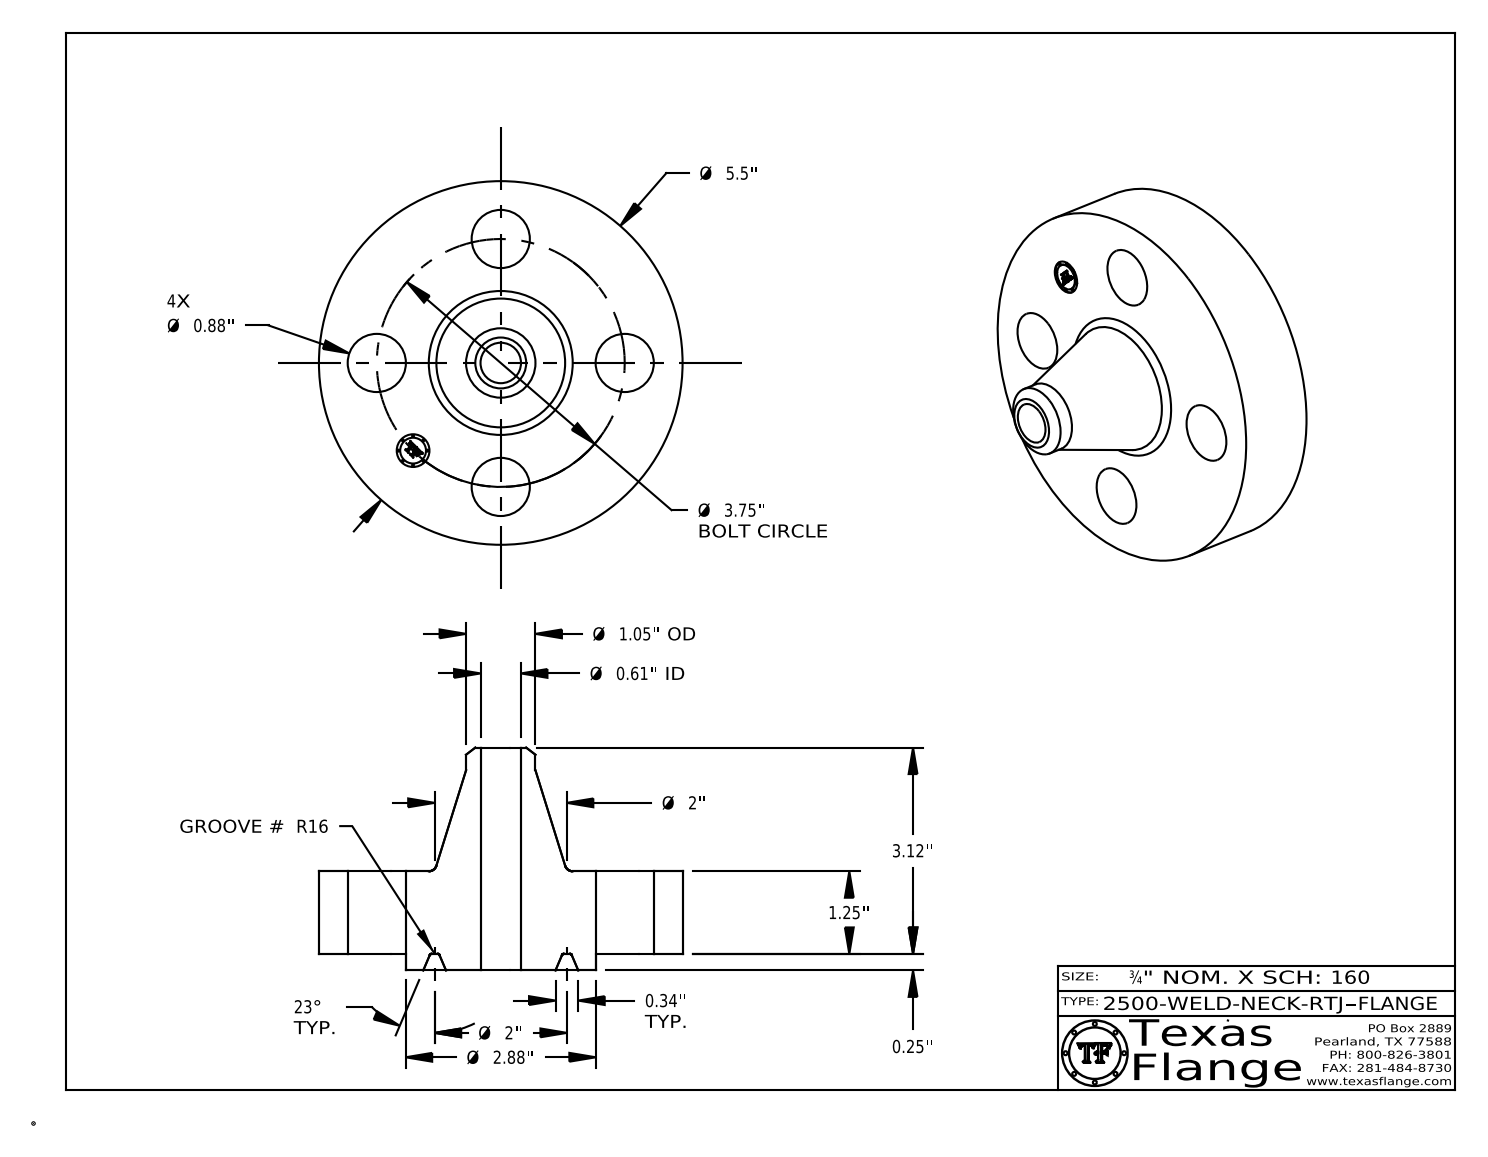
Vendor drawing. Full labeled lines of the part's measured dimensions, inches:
Part name (STEP PRODUCT): 2500-WELD-NECK-RTJ
STEP written by: CATIA V5 STEP AP214 (AUTOMOTIVE_DESIGN)
Units: inches
Bodies: 1 solid, 425 faces (371 planar, 40 cylindrical, 14 other)
Overall size (bounding box): 5.5 × 5.5 × 3.37
Volume: 30.08 in³ · Surface area: 94.45 in²
Round holes (diameter × count): ⌀0.88 ×4, ⌀0.495 ×1, ⌀0.612 ×1
Round bosses / shafts (diameter × count): ⌀0.03 ×8, ⌀5.5 ×1, ⌀2.875 ×1, ⌀1.05 ×1, ⌀0.39 ×1
Main face-to-face distances: 1.25, 0.25, 1.5, 3.37, 3.12, 1.87, 1.485, 1.235, 0.015, 1.885
Hole centre spacings: 1.875, 2.652, 1.435, 3.465, 3.75
